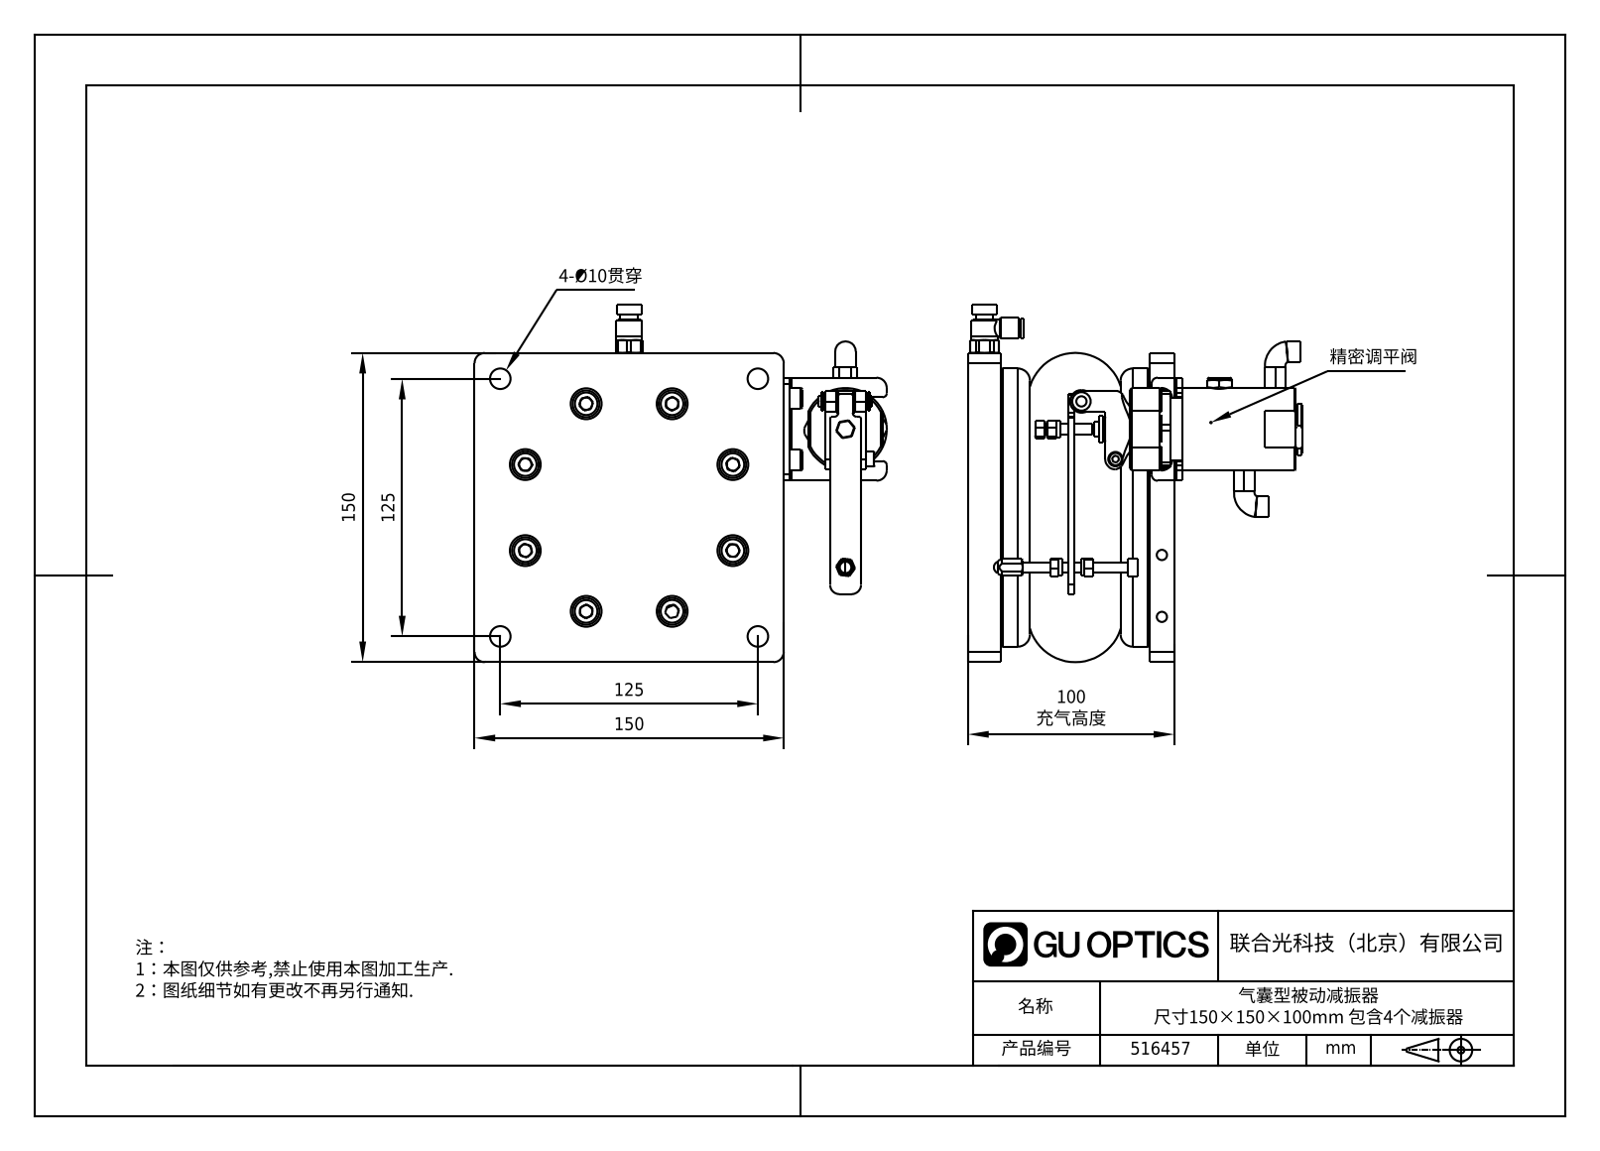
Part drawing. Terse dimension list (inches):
name: 516457
written by: SolidWorks 2020 (CONFIG_CONTROL_DESIGN)
unit: in
bodies: 0 solids, 497 faces (303 planar, 124 cylindrical, 70 other)
size: 7.874 × 6.831 × 5.886
holes: 8× ⌀0.591, 5× ⌀0.197, 4× ⌀0.394, 2× ⌀0.276, 2× ⌀0.453, 1× ⌀0.382, 1× ⌀0.433, 1× ⌀0.512, 1× ⌀5.315
bosses: 4× ⌀0.512, 3× ⌀0.315, 2× ⌀0.394, 2× ⌀0.276, 2× ⌀0.197, 1× ⌀1.89, 1× ⌀1.575, 1× ⌀1.181
rounds: 10× R0.197, 6× R0.012, 4× R0.079, 2× R0.118, 2× R0.177, 1× R0.029, 1× R0.147, 1× R0.276
face distances: 0.472, 0.63, 3.307, 2.835, 3.465, 3.937, 2.283, 0.551, 5.906, 1.181
hole spacings: 2.146, 4.736, 1.642, 3.034, 3.965, 1.708, 1.708, 3.316
